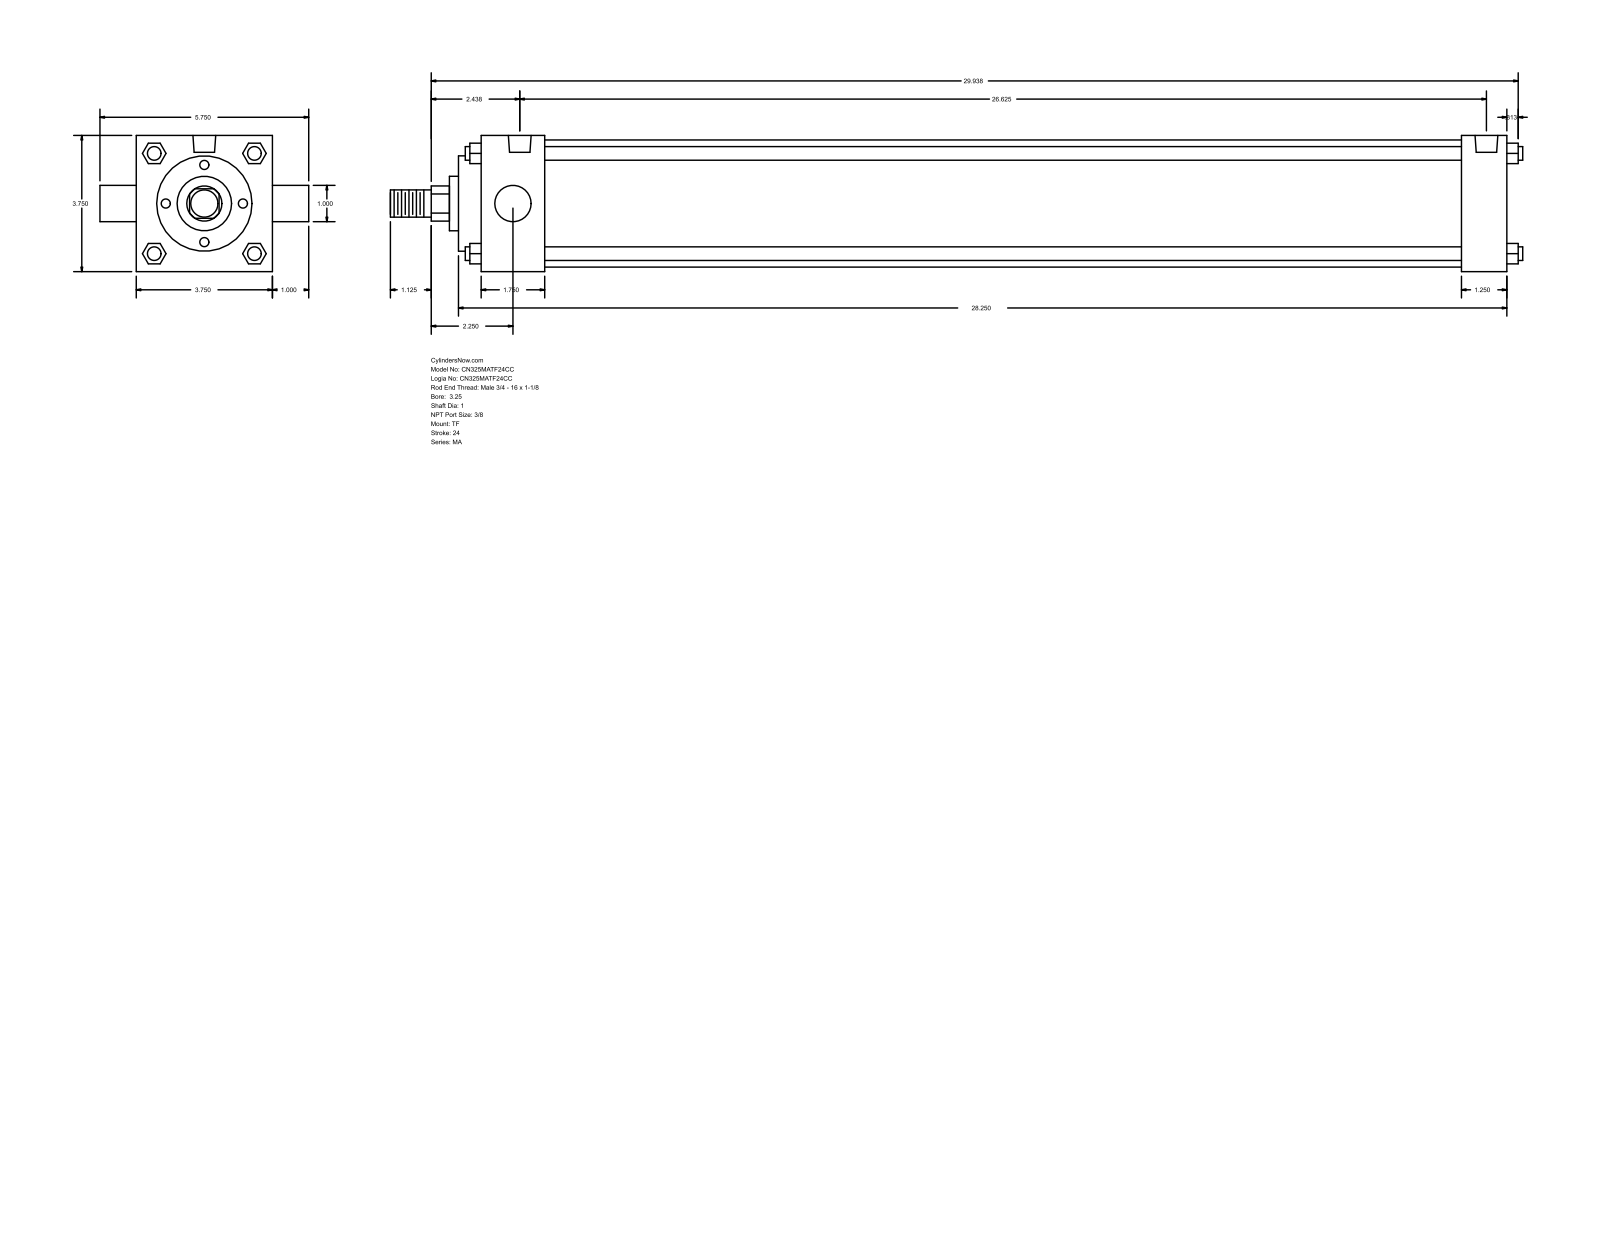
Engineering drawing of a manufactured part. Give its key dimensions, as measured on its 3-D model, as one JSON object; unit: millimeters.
{"part_name": "MA_TF__0325_1", "step_written_by": "GSSL Pune (CONFIG_CONTROL_DESIGN)", "units": "millimeters", "bodies": {"solids": 0, "faces": 122, "planar": 93, "cylindrical": 29, "other": 0}, "overall_size": [792.16, 146.05, 95.25], "round_holes": [[11.11, 3], [15.93, 2]], "round_bosses_or_shafts": [[9.53, 4], [25.4, 2], [88.9, 1], [66.67, 1], [38.1, 1], [19.05, 1]], "partial_cylinders_radius": [[12.29, 1]], "face_to_face_distances": [95.24, 717.56, 44.46, 685.81, 641.35, 673.1, 31.75, 15.87, 60.33, 701.68], "hole_center_spacings": [4.76, 4.77, 666.75, 671.51, 671.52, 676.28]}
